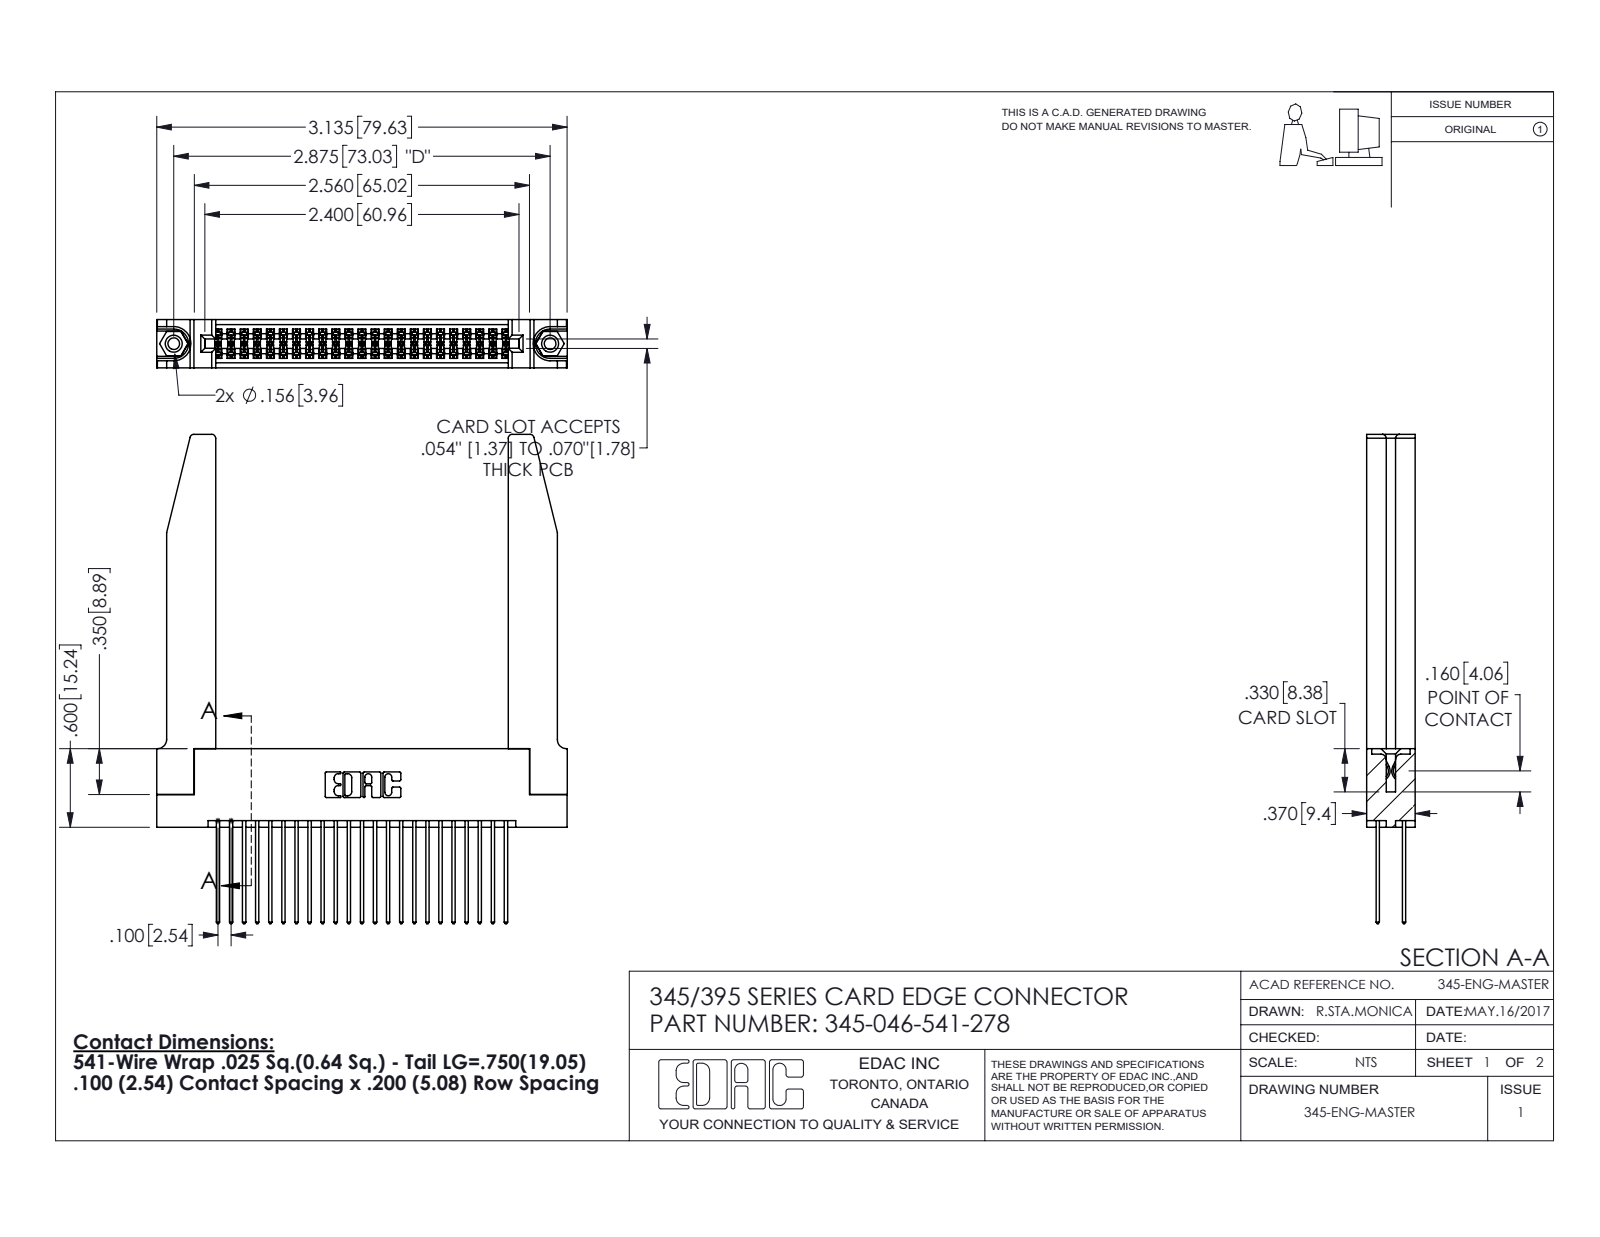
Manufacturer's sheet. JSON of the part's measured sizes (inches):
{"part_name": "345-220-078_345-220-078; 345 Part_Flush Mounting Lugs - 0.156 Dia-TH; 345-250-001_345-250-001-102; 345-046-541-278 (+1 more)", "step_written_by": "SolidWorks 2016 (CONFIG_CONTROL_DESIGN)", "units": "inches", "bodies": {"solids": 51, "faces": 2660, "planar": 1740, "cylindrical": 868, "other": 52}, "overall_size": [3.737, 3.136, 0.37], "volume_in3": 0.952, "surface_area_in2": 29.88, "round_holes": [[0.089, 2], [0.125, 2], [0.156, 2], [0.064, 1]], "round_bosses_or_shafts": [[0.155, 2]], "partial_cylinders_radius": [[0.006, 69], [0.01, 46], [0.01, 22], [0.03, 8], [0.007, 6], [0.031, 6], [0.026, 3], [0.014, 2]], "face_to_face_distances": [0.37, 0.072, 0.298, 0.2, 0.098, 0.272, 0.025, 0.225, 0.175, 0.148], "hole_center_spacings": [0.27, 2.641, 2.875]}
